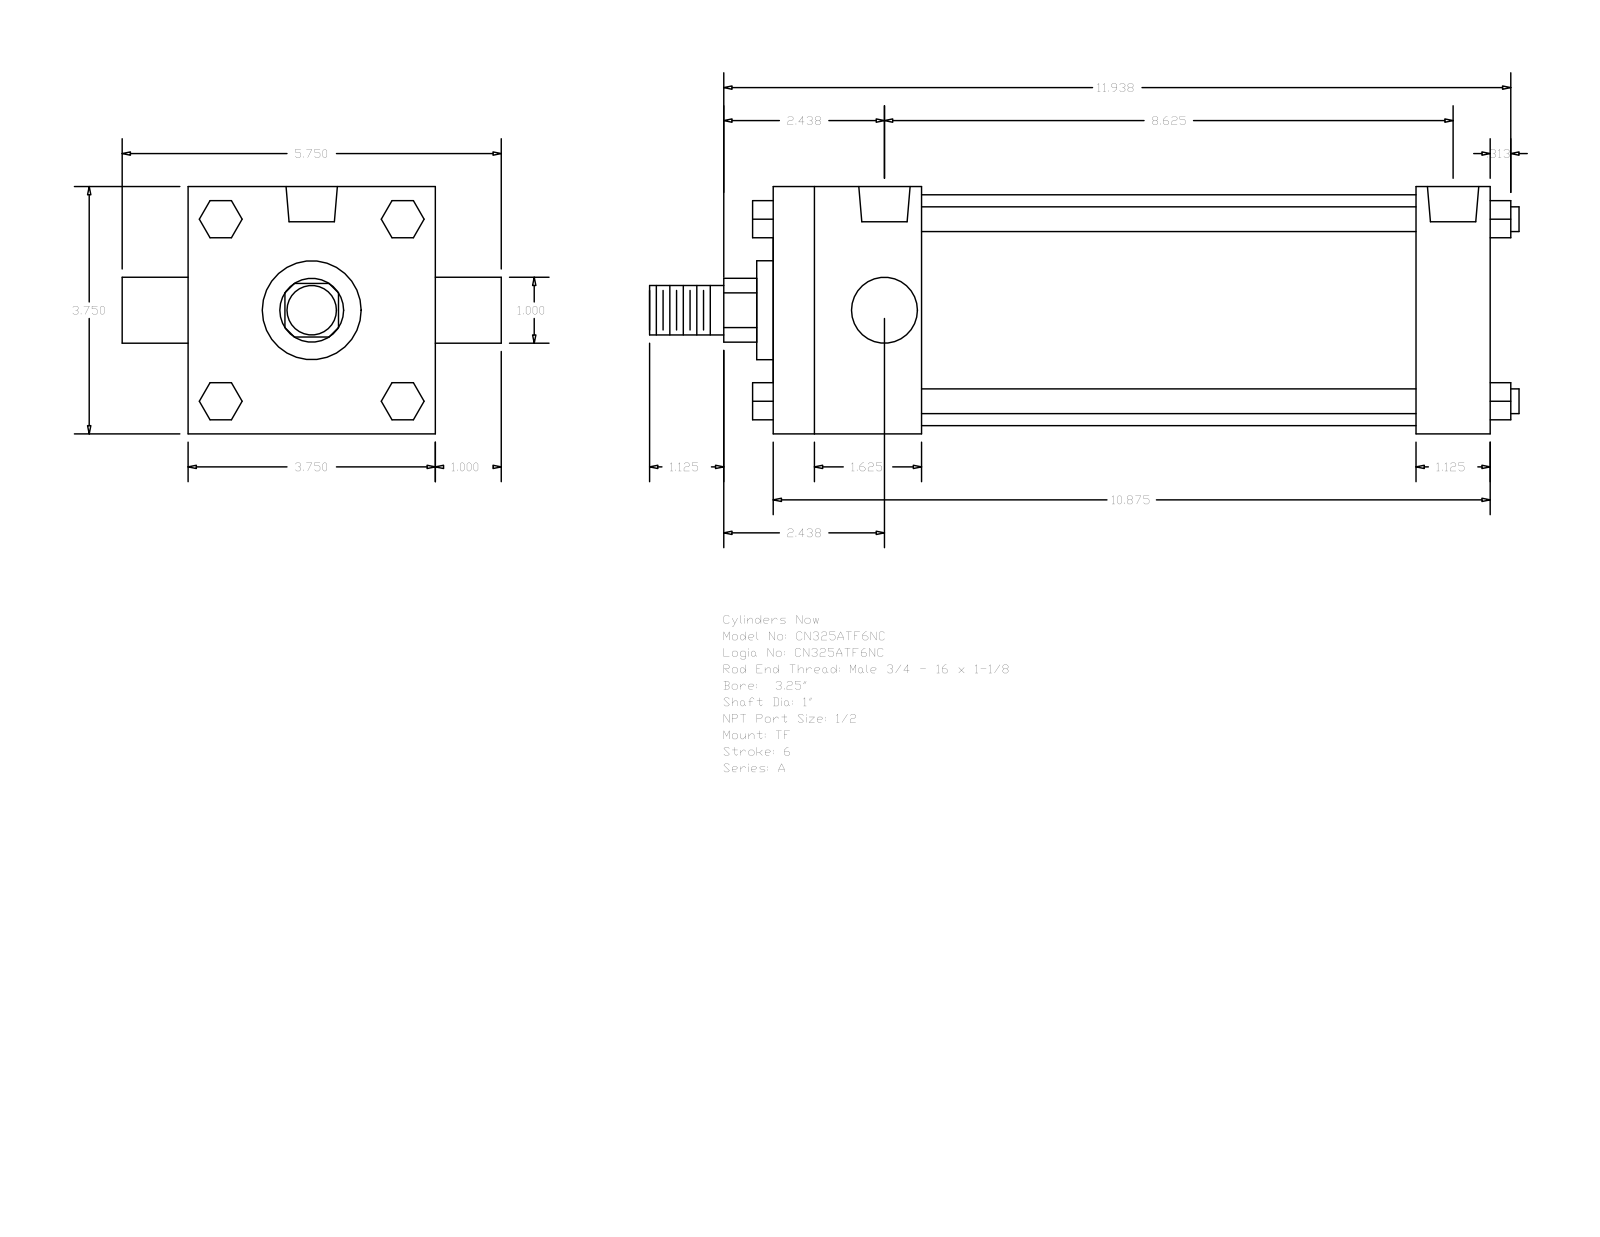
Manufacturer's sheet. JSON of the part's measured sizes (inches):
{"part_name": "A_TF__0325_1", "step_written_by": "GSSL Pune (CONFIG_CONTROL_DESIGN)", "units": "inches", "bodies": {"solids": 0, "faces": 120, "planar": 92, "cylindrical": 28, "other": 0}, "overall_size": [13.187, 5.75, 3.75], "round_holes": [[0.344, 3], [0.778, 2]], "round_bosses_or_shafts": [[0.375, 4], [1, 2], [3.5, 1], [1.5, 1], [0.75, 1]], "partial_cylinders_radius": [[0.484, 1]], "face_to_face_distances": [3.75, 10.875, 1.125, 2.25, 9.75, 7.5, 8.625, 0.562, 1.38, 2.39], "hole_center_spacings": [0.125, 8.5, 8.375, 8.625]}
